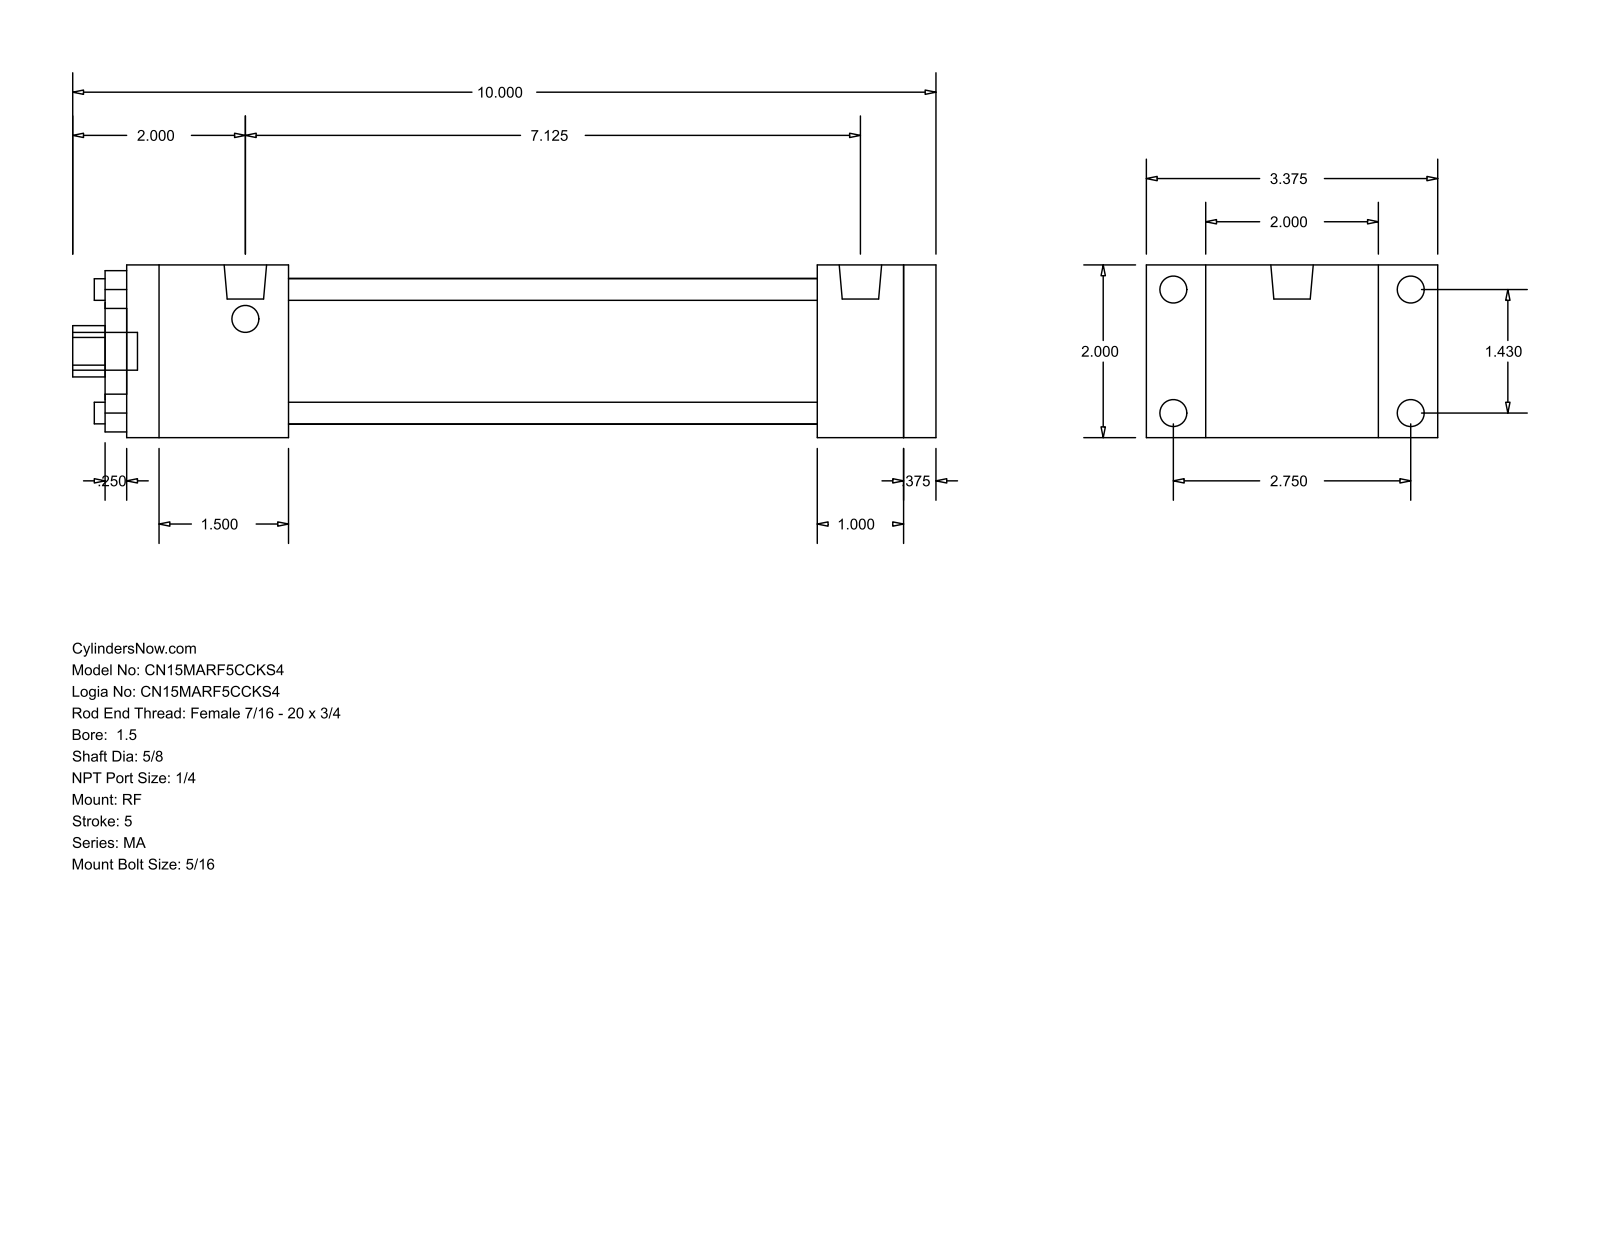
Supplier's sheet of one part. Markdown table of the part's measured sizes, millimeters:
| quantity | value |
| --- | --- |
| part name | MA_RF__0150_0.625 |
| STEP written by | GSSL Pune (CONFIG_CONTROL_DESIGN) |
| units | millimeters |
| bodies | 0 solids, 92 faces (64 planar, 28 cylindrical, 0 other) |
| overall size | 254 × 85.72 × 50.8 |
| round holes (diameter × count) | 6.35 × 4, 15.88 × 1, 28.57 × 1, 42.93 × 1 |
| round bosses / shafts (diameter × count) | 7.94 × 8, 12.49 × 2, 11.11 × 1 |
| partial cylindrical surfaces (radius × count) | 7.54 × 1 |
| main face-to-face distances | 50.8, 9.53, 238.12, 228.59, 203.19, 25.4, 34.93, 47.62, 155.57, 180.97 |
| hole center spacings | 25.68, 36.32, 51.36 |
